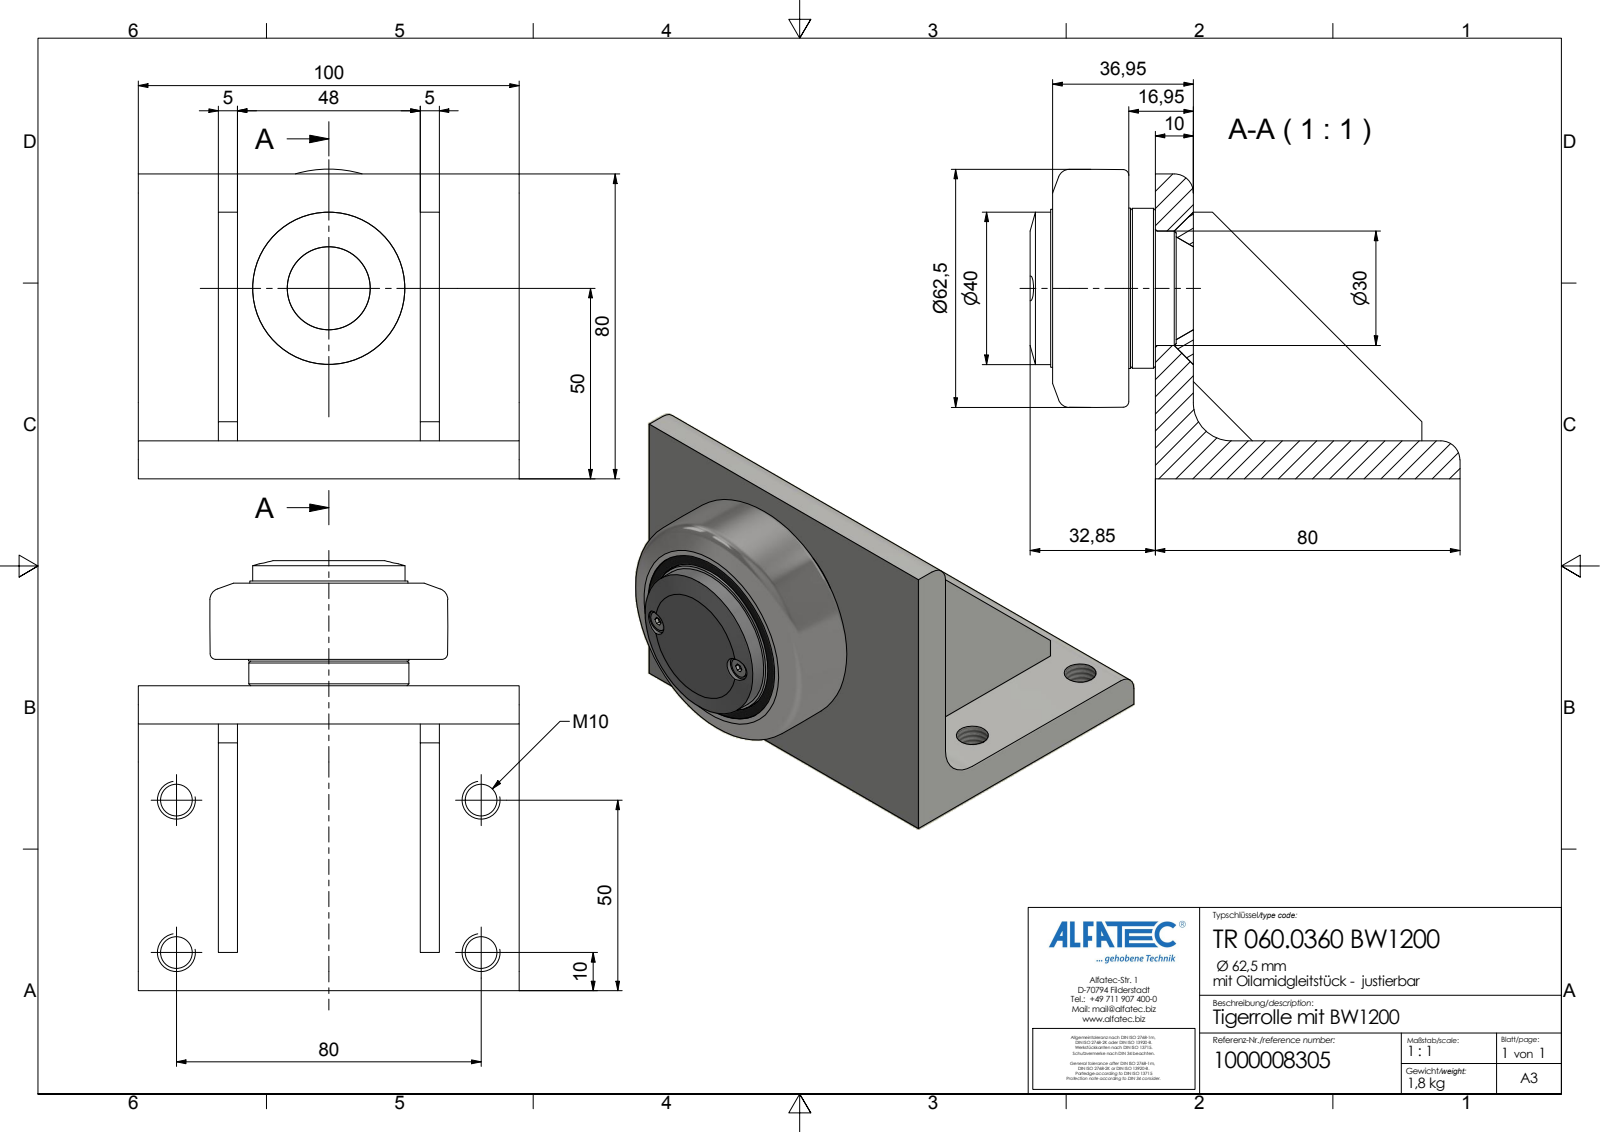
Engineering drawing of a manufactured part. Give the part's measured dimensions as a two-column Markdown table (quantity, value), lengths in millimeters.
| quantity | value |
| --- | --- |
| part name | TR 060.0360 BW1200_Kontur |
| STEP written by | Autodesk Inventor 2020 (AP242_MANAGED_MODEL_BASED_3D_ENGINEERING_MIM_LF) |
| units | millimeters |
| bodies | 1 solid, 77 faces (46 planar, 19 cylindrical, 12 other) |
| overall size | 113 × 100 × 81.25 |
| volume | 244 604 mm³ |
| surface area | 51 934 mm² |
| round holes (diameter × count) | 8.38 × 4, 6.5 × 2, 42 × 1, 42.97 × 1, 47 × 1 |
| round bosses / shafts (diameter × count) | 5.35 × 2, 42.1 × 1, 41.5 × 1, 40 × 1 |
| partial cylindrical surfaces (radius × count) | 5 × 2, 10 × 1 |
| main face-to-face distances | 10, 5, 53, 21, 26, 74, 79, 58, 48, 100 |
| hole center spacings | 15, 40, 80, 89.44, 30 |
